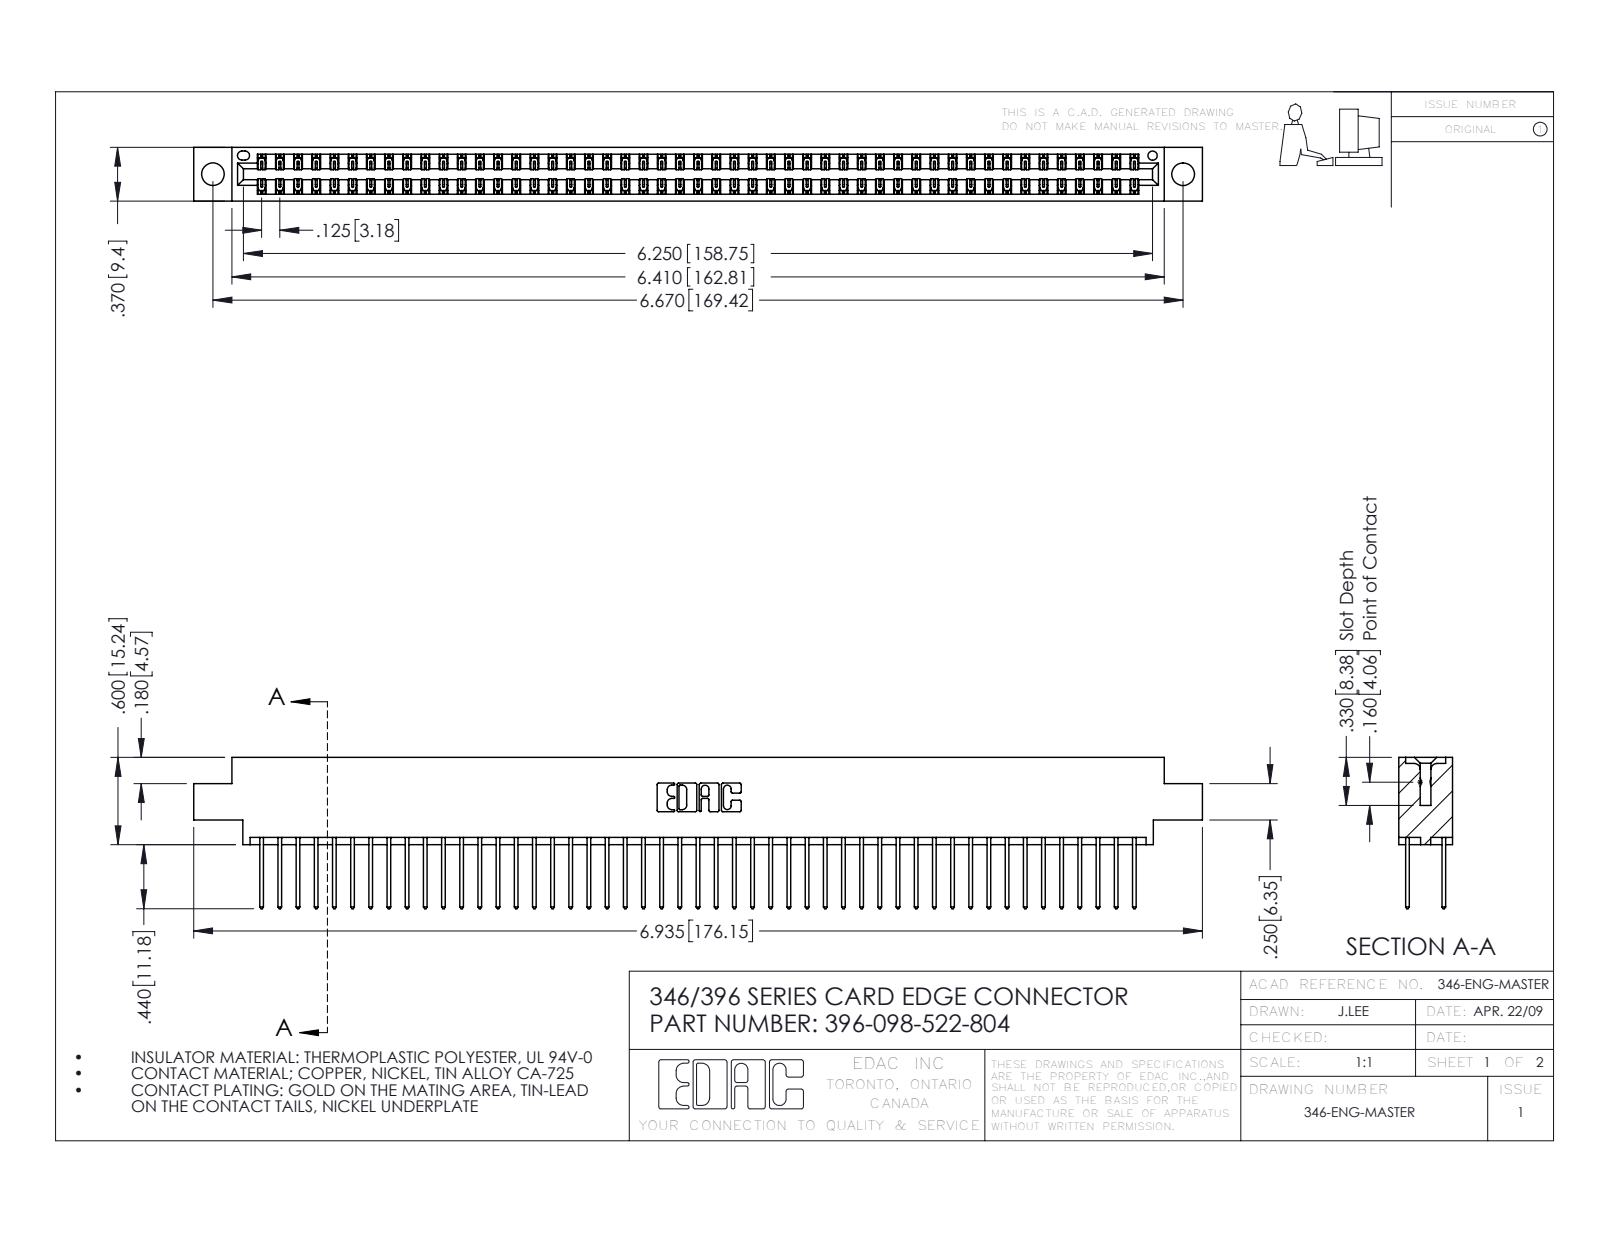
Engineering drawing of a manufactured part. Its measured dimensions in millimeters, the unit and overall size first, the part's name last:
Units: millimetres
Overall size (bounding box): 176.1 × 26.4 × 9.4
Round holes (diameter × count): ⌀4 ×2, ⌀1.6 ×1
Partial cylindrical surfaces — rounded edges, fillets, slot ends (radius × count): R0.2 ×147, R0.3 ×98, R0.3 ×22, R0.2 ×6, R0.8 ×6, R0.7 ×3, R0.4 ×2, R0.6 ×2
Main face-to-face distances: 1.2, 8.2, 6.4, 9.4, 1.8, 7.6, 0.6, 7, 3.8, 5.6
Hole centre spacings: 6.2, 164.1, 169.4
Volume: 17 240 mm³ · Surface area: 24 960 mm²
Bodies: 99 solids, 5222 faces (3510 planar, 1712 cylindrical, 0 other)
Part name (STEP PRODUCT): 396-098-522-804; 346 Part_0.170 Offset - 0.156 Dia-TH; 345-292-001_345-293-122
STEP written by: SolidWorks 2016 (CONFIG_CONTROL_DESIGN)
